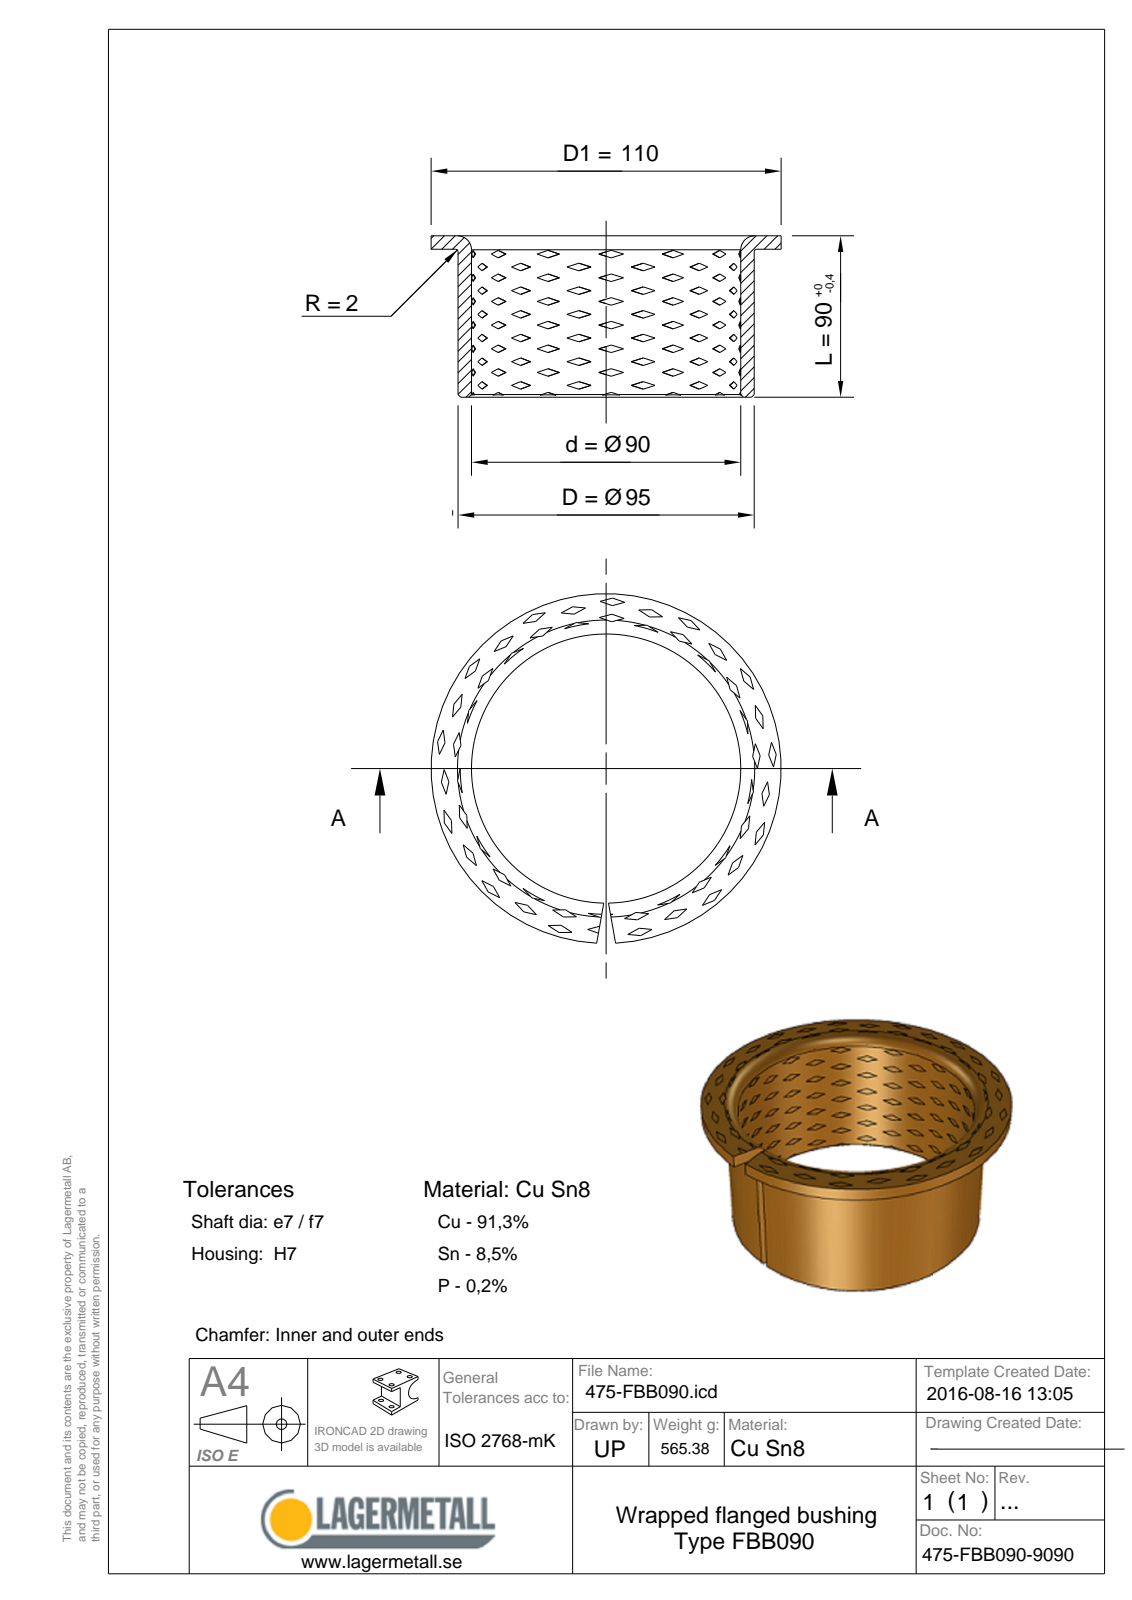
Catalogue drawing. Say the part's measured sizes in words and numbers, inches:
The part is named "475-FBB090-9090". Its 3-D file was written by "Spatial InterOp 3D (CONFIG_CONTROL_DESIGN)". It is 1 solid with 12 faces: 5 planar, 3 cylindrical and 4 other. Overall it measures 4.331 by 4.329 by 3.543 inches. Its volume is 4.259 cubic inches and its surface area 89.61 square inches. Round holes: 1 of diameter 3.543. Round bosses or shafts: 1 of diameter 4.331, 1 of diameter 3.74. The main face-to-face distances are 0.098, 3.445, 3.543.
